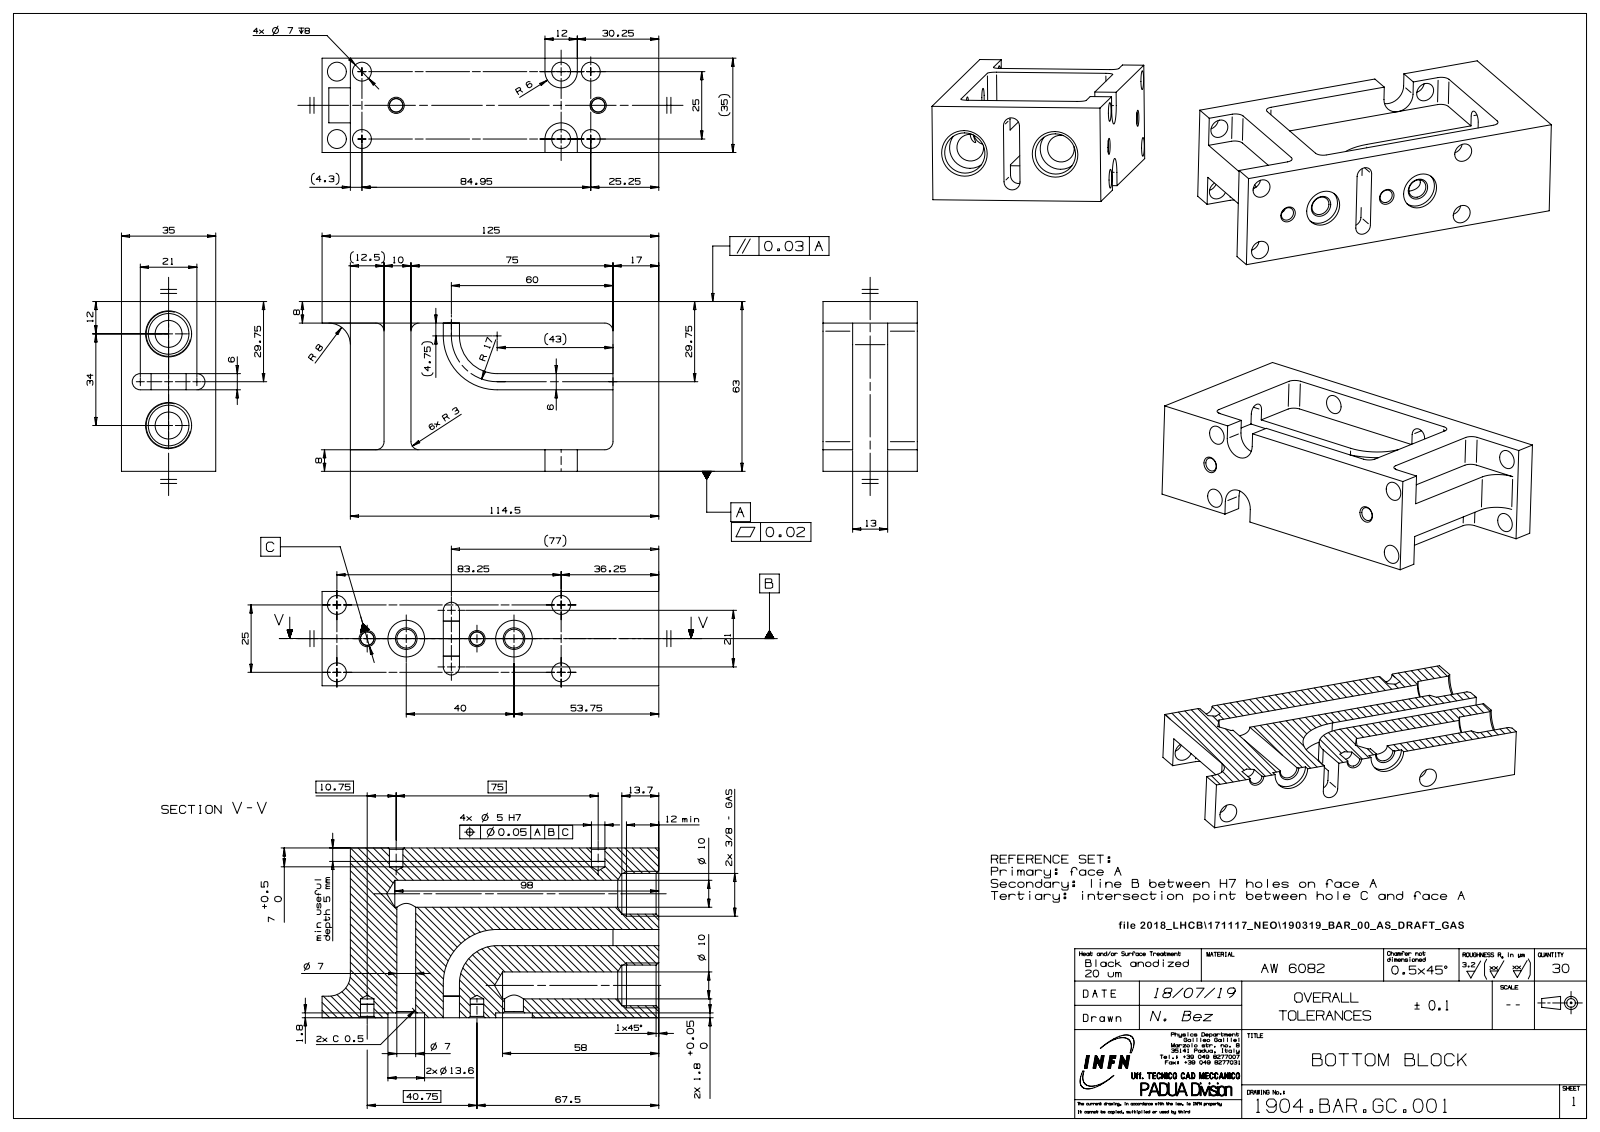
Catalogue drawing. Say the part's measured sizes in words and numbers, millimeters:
The part is named "bez0D28BFECq45f". Its 3-D file was written by "SIEMENS PLM Software NX 12.0 (AUTOMOTIVE_DESIGN)". It is 1 solid with 95 faces: 38 planar, 41 cylindrical and 16 other. Overall it measures 125 by 63 by 35 millimeters. Its volume is 133 173 cubic millimeters and its surface area 42 856 square millimeters. Round holes: 10 of diameter 7, 4 of diameter 5, 2 of diameter 10, 2 of diameter 13.6, 2 of diameter 15.08. Partial cylindrical surfaces (rounded edges, fillets, slot ends): 10 of radius 3, 2 of radius 6, 1 of radius 8, 1 of radius 14, 1 of radius 20. The main face-to-face distances are 11, 24, 63, 13, 35, 8, 55, 47, 6, 30.25. The hole center spacings are 25, 9.3, 11, 12.65, 12.8, 16.82, 17.82, 18.58.
